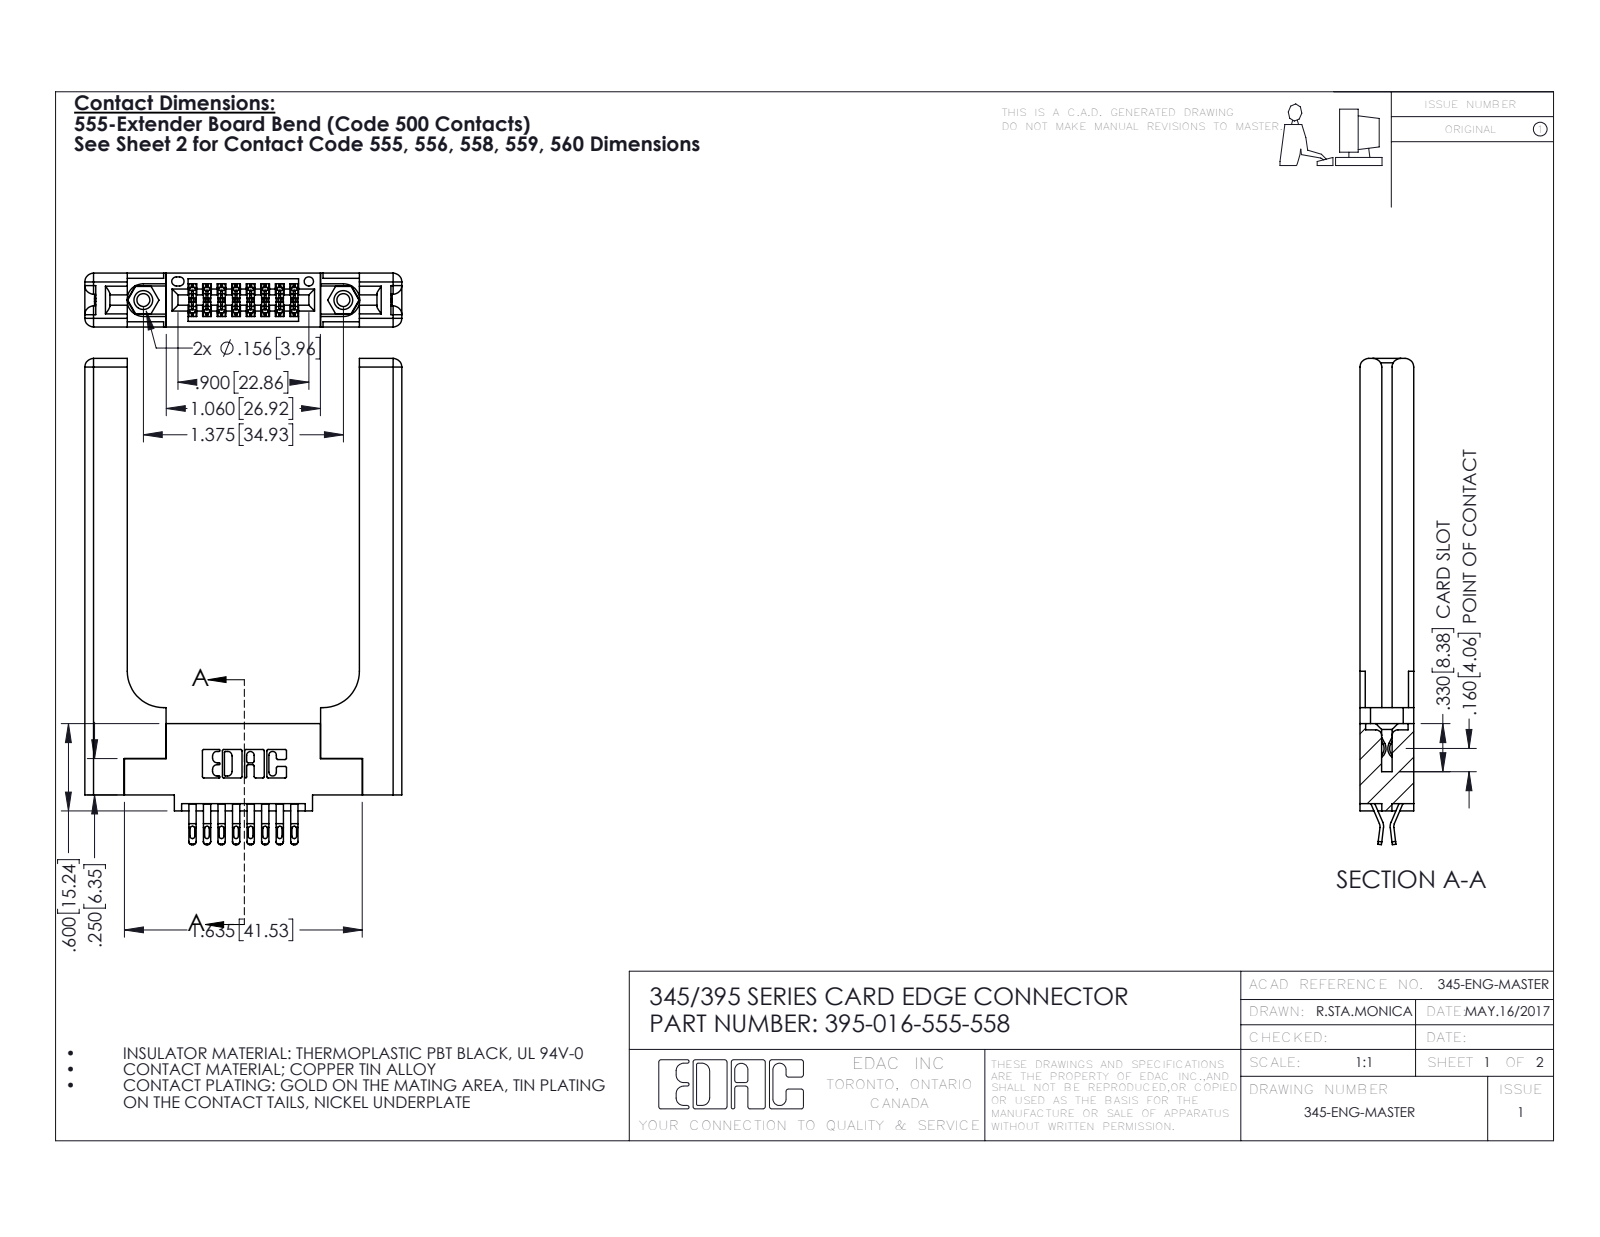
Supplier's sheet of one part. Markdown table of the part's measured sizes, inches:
| quantity | value |
| --- | --- |
| part name | 345-250-001_345-250-001-102; 345-292-001_555 Tail; 345-220-058_345-220-058; 345 Part_0.110 Offset - 0.156 Dia-TH (+1 more) |
| STEP written by | SolidWorks 2016 (CONFIG_CONTROL_DESIGN) |
| units | inches |
| bodies | 21 solids, 1282 faces (728 planar, 494 cylindrical, 60 other) |
| overall size | 3.342 × 2.179 × 0.37 |
| volume | 0.824 in³ |
| surface area | 18.75 in² |
| round holes (diameter × count) | 0.089 × 2, 0.125 × 2, 0.156 × 2, 0.064 × 1 |
| round bosses / shafts (diameter × count) | 0.155 × 2 |
| partial cylindrical surfaces (radius × count) | 0.016 × 40, 0.02 × 32, 0.006 × 24, 0.01 × 22, 0.06 × 16, 0.007 × 6, 0.031 × 6, 0.026 × 3 |
| main face-to-face distances | 0.37, 0.15, 0.22, 0.072, 0.148, 0.077, 0.298, 1.596, 0.071, 0.225 |
| hole center spacings | 0.27, 1.144, 1.375 |
